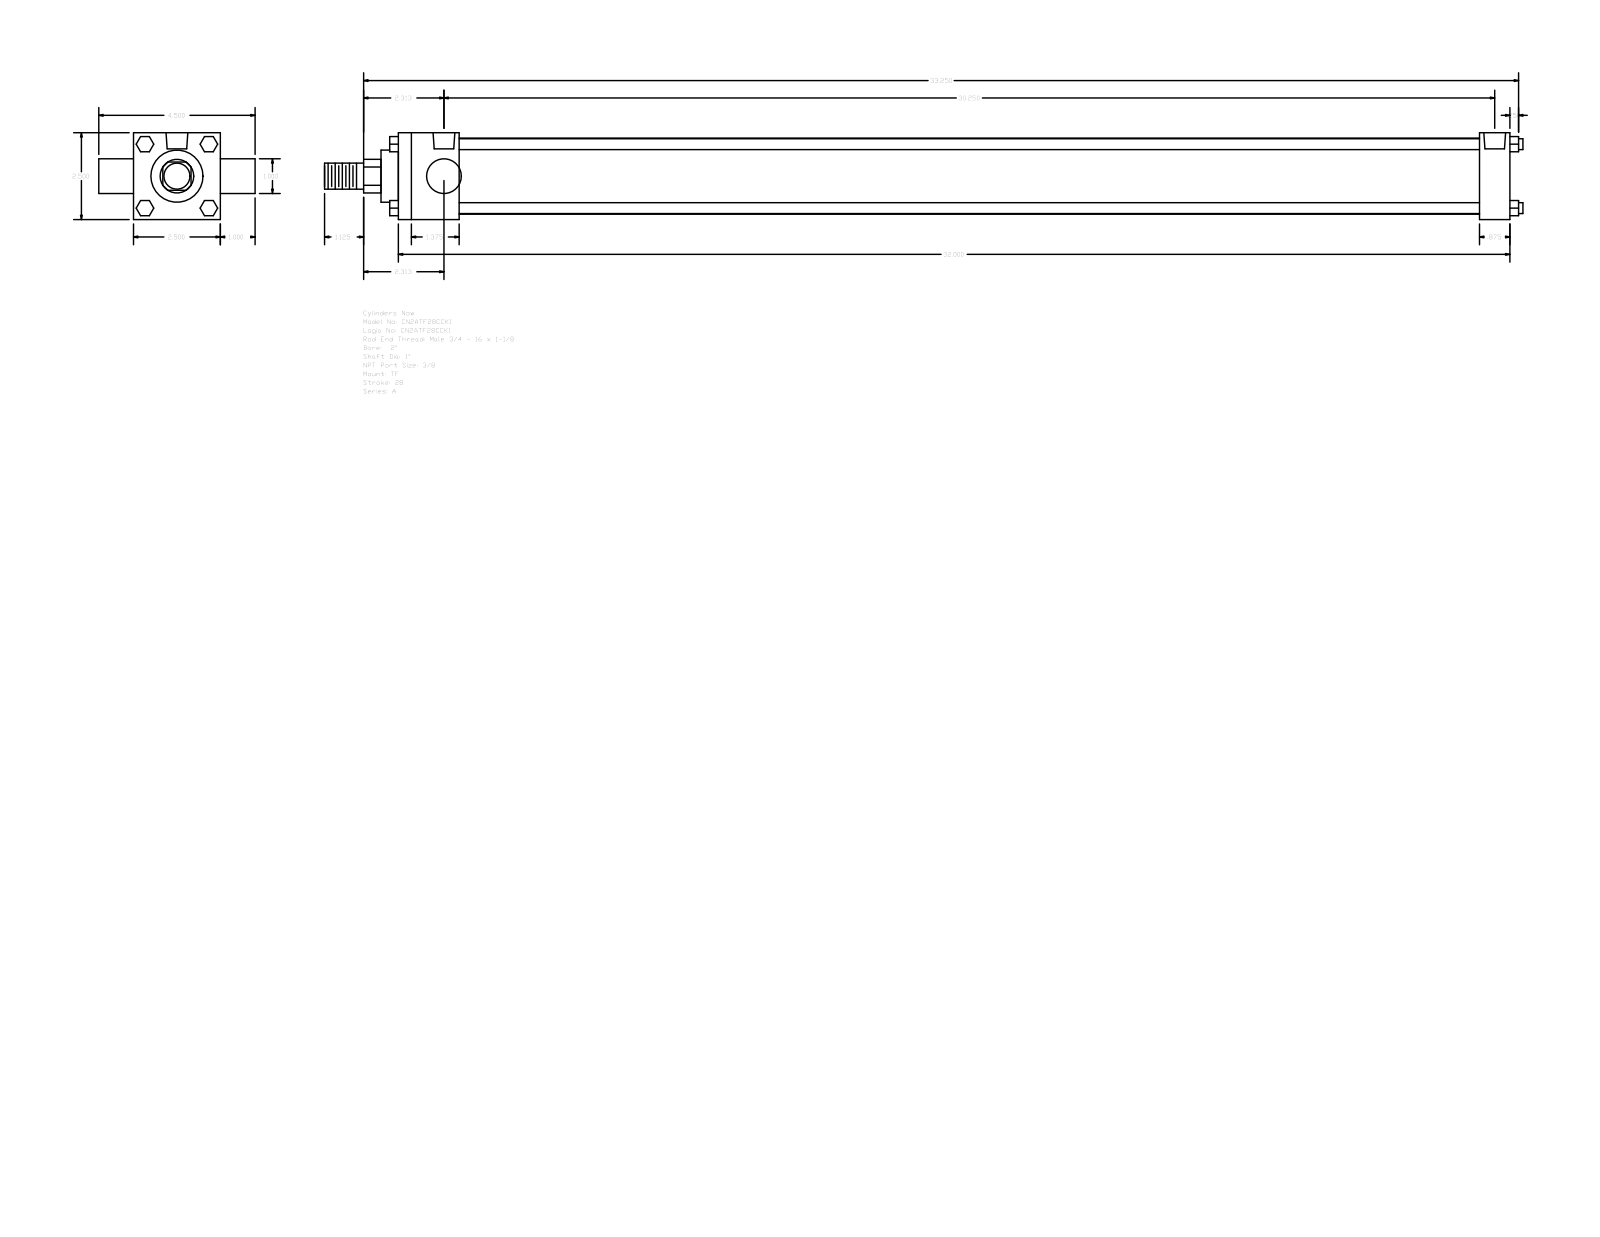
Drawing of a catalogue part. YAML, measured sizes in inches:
part_name: "A_TF__0200_1"
step_written_by: "GSSL Pune (CONFIG_CONTROL_DESIGN)"
units: inches
bodies: {solids: 0, faces: 120, planar: 92, cylindrical: 28, other: 0}
overall_size: [34.5, 4.5, 2.5]
round_holes:
  - {diameter: 0.219, count: 3}
  - {diameter: 0.627, count: 2}
round_bosses_or_shafts:
  - {diameter: 0.313, count: 4}
  - {diameter: 1, count: 2}
  - {diameter: 2.19, count: 1}
  - {diameter: 1.5, count: 1}
  - {diameter: 0.75, count: 1}
partial_cylinders:
  - {radius: 0.484, count: 1}
face_to_face_distances: [2.5, 32, 1.75, 31.125, 29.375, 30.25, 0.875, 1, 3.5, 32.5]
hole_center_spacings: [0.063, 0.157, 30.031, 30.093, 30.187, 30.25]
